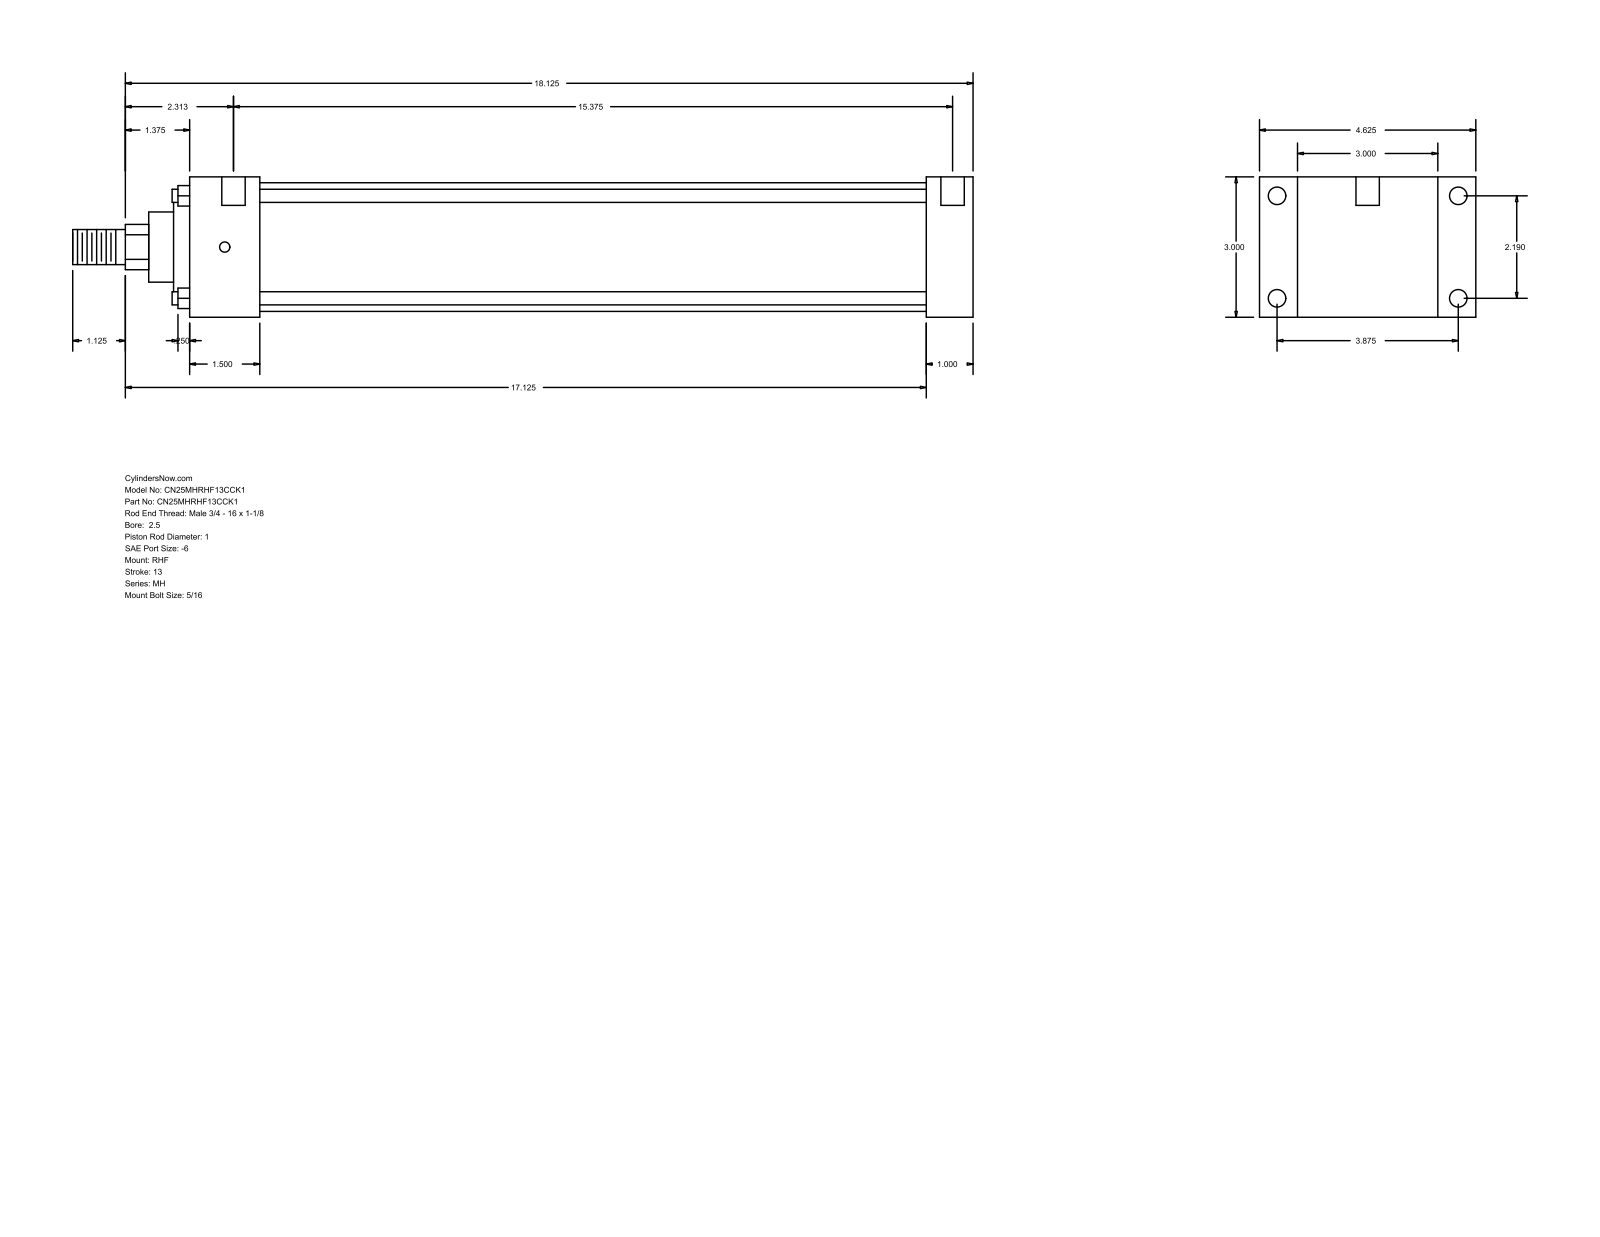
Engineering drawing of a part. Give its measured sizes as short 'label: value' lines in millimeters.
name: MH_RHF__0250_1
written by: GSSL Pune (CONFIG_CONTROL_DESIGN)
unit: mm
bodies: 0 solids, 90 faces (61 planar, 29 cylindrical, 0 other)
size: 488.95 × 117.47 × 76.2
holes: 4× ⌀5.56, 4× ⌀9.53, 2× ⌀12.7
bosses: 4× ⌀7.14, 1× ⌀69.85, 1× ⌀60.33, 1× ⌀38.1, 1× ⌀25.4, 1× ⌀19.05
rounds: 1× R12.29
face distances: 76.2, 25.4, 20.64, 96.84, 400.06, 425.46, 117.48, 38.11, 361.95, 387.35
hole spacings: 55.62, 98.42, 113.05, 398.46, 3.18, 4.76, 390.52, 393.7
